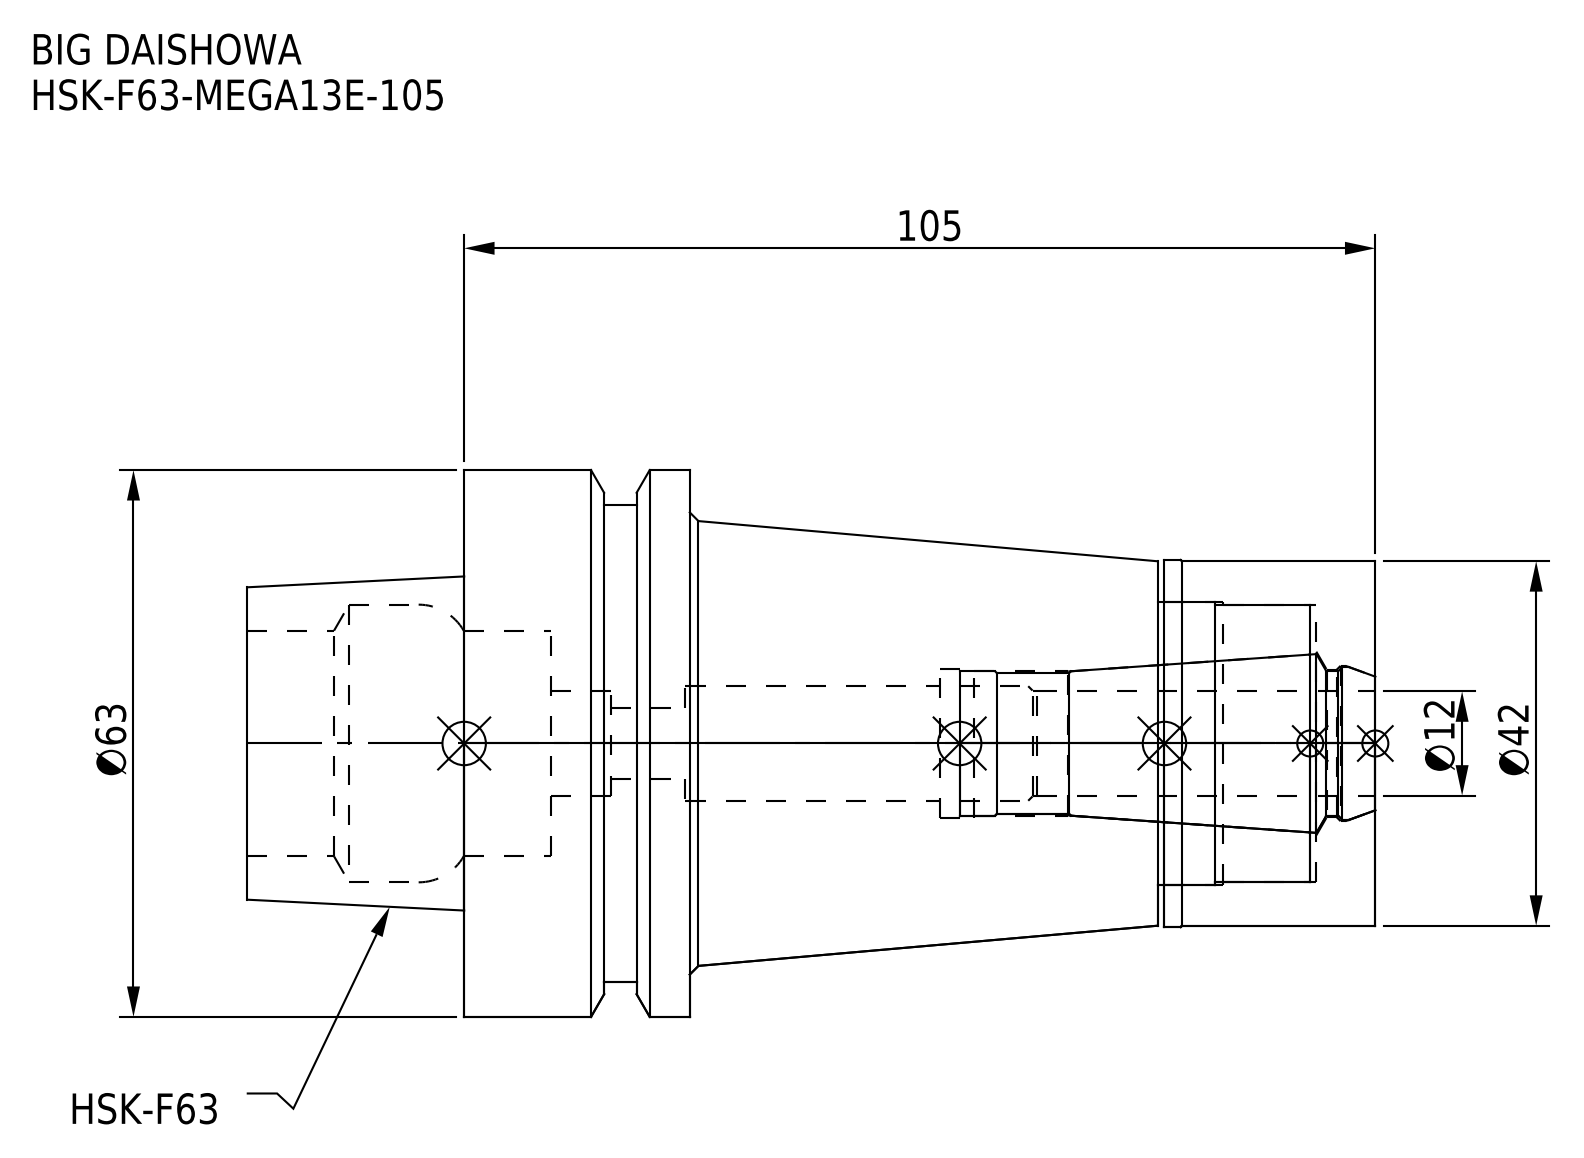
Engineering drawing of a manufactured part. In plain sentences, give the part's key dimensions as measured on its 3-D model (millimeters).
The part is named "HSK-F63-MEGA13E-105-120.stp; HSK-F63-MEGA13E-105_1.stp; DXF_TEMP_ASSY_ASM_4_ASM.stp; HSK-F63-MEGA13E-105-120-FreeParts (+3 more)". Its 3-D file was written by "SolidWorks 2019 (CONFIG_CONTROL_DESIGN)". It is 2 solids with 81 faces: 17 planar, 40 cylindrical and 24 other. Overall it measures 130 by 63 by 63 millimeters. Its volume is 191 602 cubic millimeters and its surface area 39 037 square millimeters. Round holes: 1 of diameter 8.25, 1 of diameter 12, 1 of diameter 13.3, 1 of diameter 16.6, 1 of diameter 17, 1 of diameter 17.2, 1 of diameter 17.9, 1 of diameter 26, 1 of diameter 32, 1 of diameter 32.5. Round bosses or shafts: 1 of diameter 63, 1 of diameter 55, 1 of diameter 42.3, 1 of diameter 42. The main face-to-face distances are 105, 79, 26, 25.1, 24.3, 54.7, 80.7, 0.8, 53.9, 79.9.
